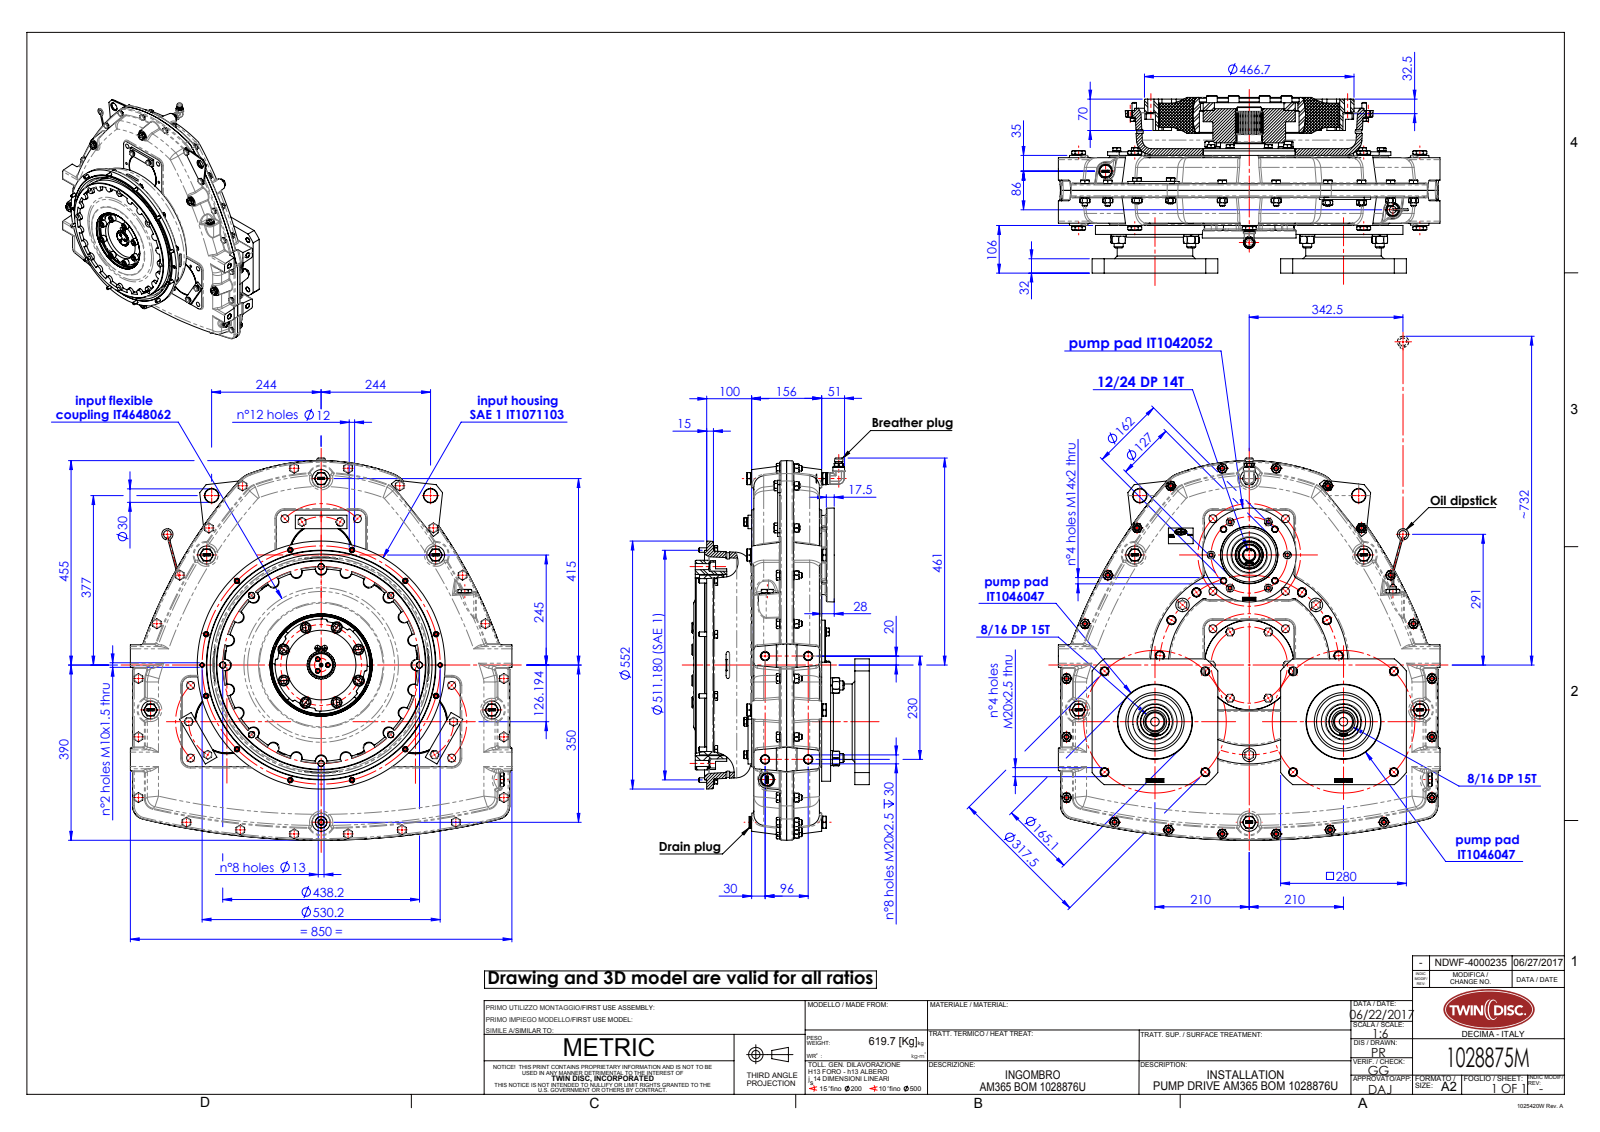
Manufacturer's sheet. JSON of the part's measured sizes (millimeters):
{"part_name": "ITam365-006_rev00-installation; ITam365-001_rev01-installation; ITB01000000_rev01-installation; ITam365-002_rev00-installation (+8 more)", "step_written_by": "SolidWorks 2015 (AUTOMOTIVE_DESIGN)", "units": "millimeters", "bodies": {"solids": 175, "faces": 10515, "planar": 4390, "cylindrical": 2814, "other": 3311}, "overall_size": [850.8, 850, 395.2], "volume_mm3": 94400000, "surface_area_mm2": 7380000, "round_holes": [[17.5, 38], [13, 36], [8.5, 29], [21, 26], [12.2, 25], [10.2, 24], [12, 23], [10.3, 21], [11, 16], [14, 16], [20.2, 16], [17, 15]], "round_bosses_or_shafts": [[10, 31], [21.1, 25], [18, 25], [20, 24], [18.1, 24], [16.2, 24], [12, 21], [33.6, 16]], "partial_cylinders_radius": [[12.5, 72], [0.35, 58], [0.45, 58], [26.41, 58], [29.53, 58], [3, 56], [2, 54], [2.5, 46]], "face_to_face_distances": [78, 73, 151, 5, 93, 15, 146, 156, 20, 171], "hole_center_spacings": [346.41, 814, 83.16, 297.26, 235.12, 45.28, 65.8, 75]}
